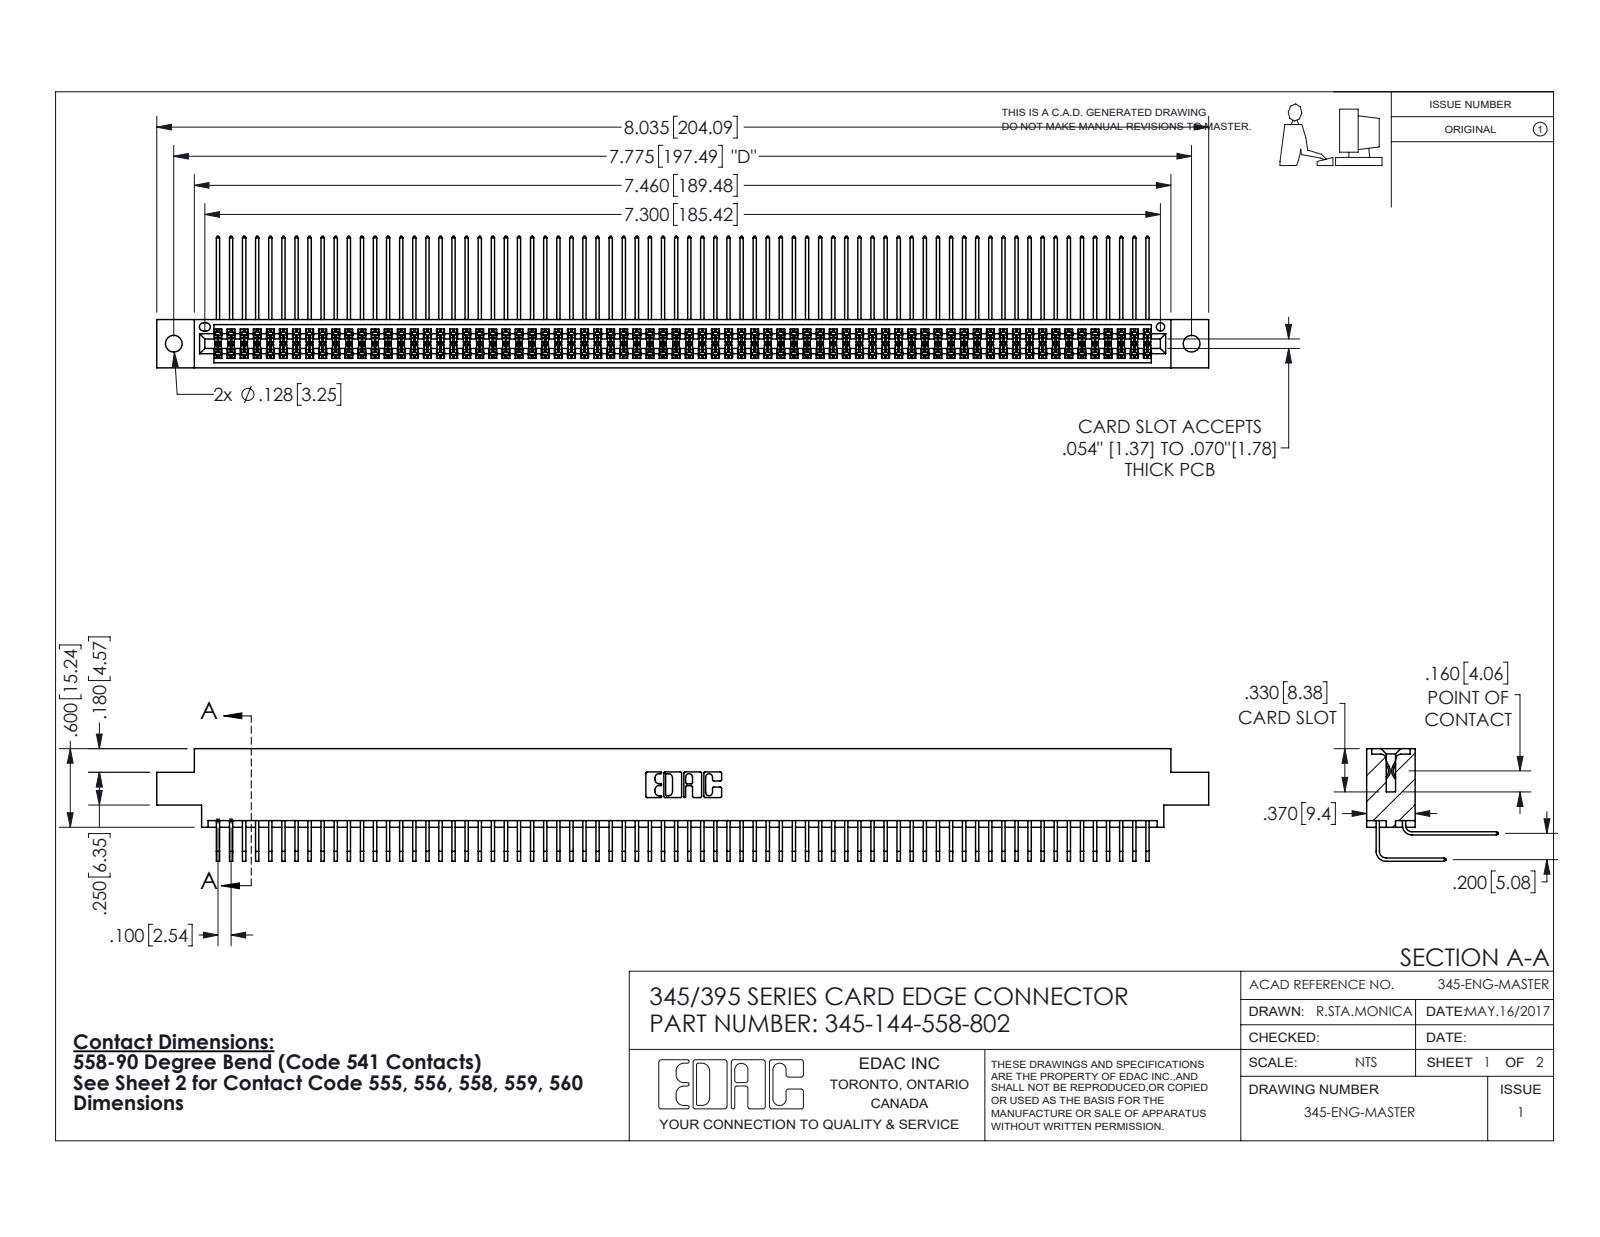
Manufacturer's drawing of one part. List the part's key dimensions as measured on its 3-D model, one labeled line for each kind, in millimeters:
Part name (STEP PRODUCT): 345-144-558-802; 345-292-001_558 Tail - 2; 345-292-001_558 559 Tail - 1; 345 Part_0.170 Offset - 0.128 Dia
STEP written by: SolidWorks 2016 (CONFIG_CONTROL_DESIGN)
Units: millimetres
Bodies: 145 solids, 7618 faces (5124 planar, 2494 cylindrical, 0 other)
Overall size (bounding box): 204.1 × 25.5 × 21.8
Volume: 20 780 mm³ · Surface area: 35 080 mm²
Round holes (diameter × count): ⌀3.3 ×2, ⌀1.6 ×1
Partial cylindrical surfaces — rounded edges, fillets, slot ends (radius × count): R0.2 ×287, R0.3 ×22, R0.2 ×6, R0.8 ×6, R0.7 ×3, R0.4 ×2, R0.5 ×2, R0.6 ×2
Main face-to-face distances: 1.8, 7.6, 5.1, 9.4, 2.5, 6.9, 0.6, 5.7, 4.4, 0.6
Hole centre spacings: 6.9, 191.5, 197.5
